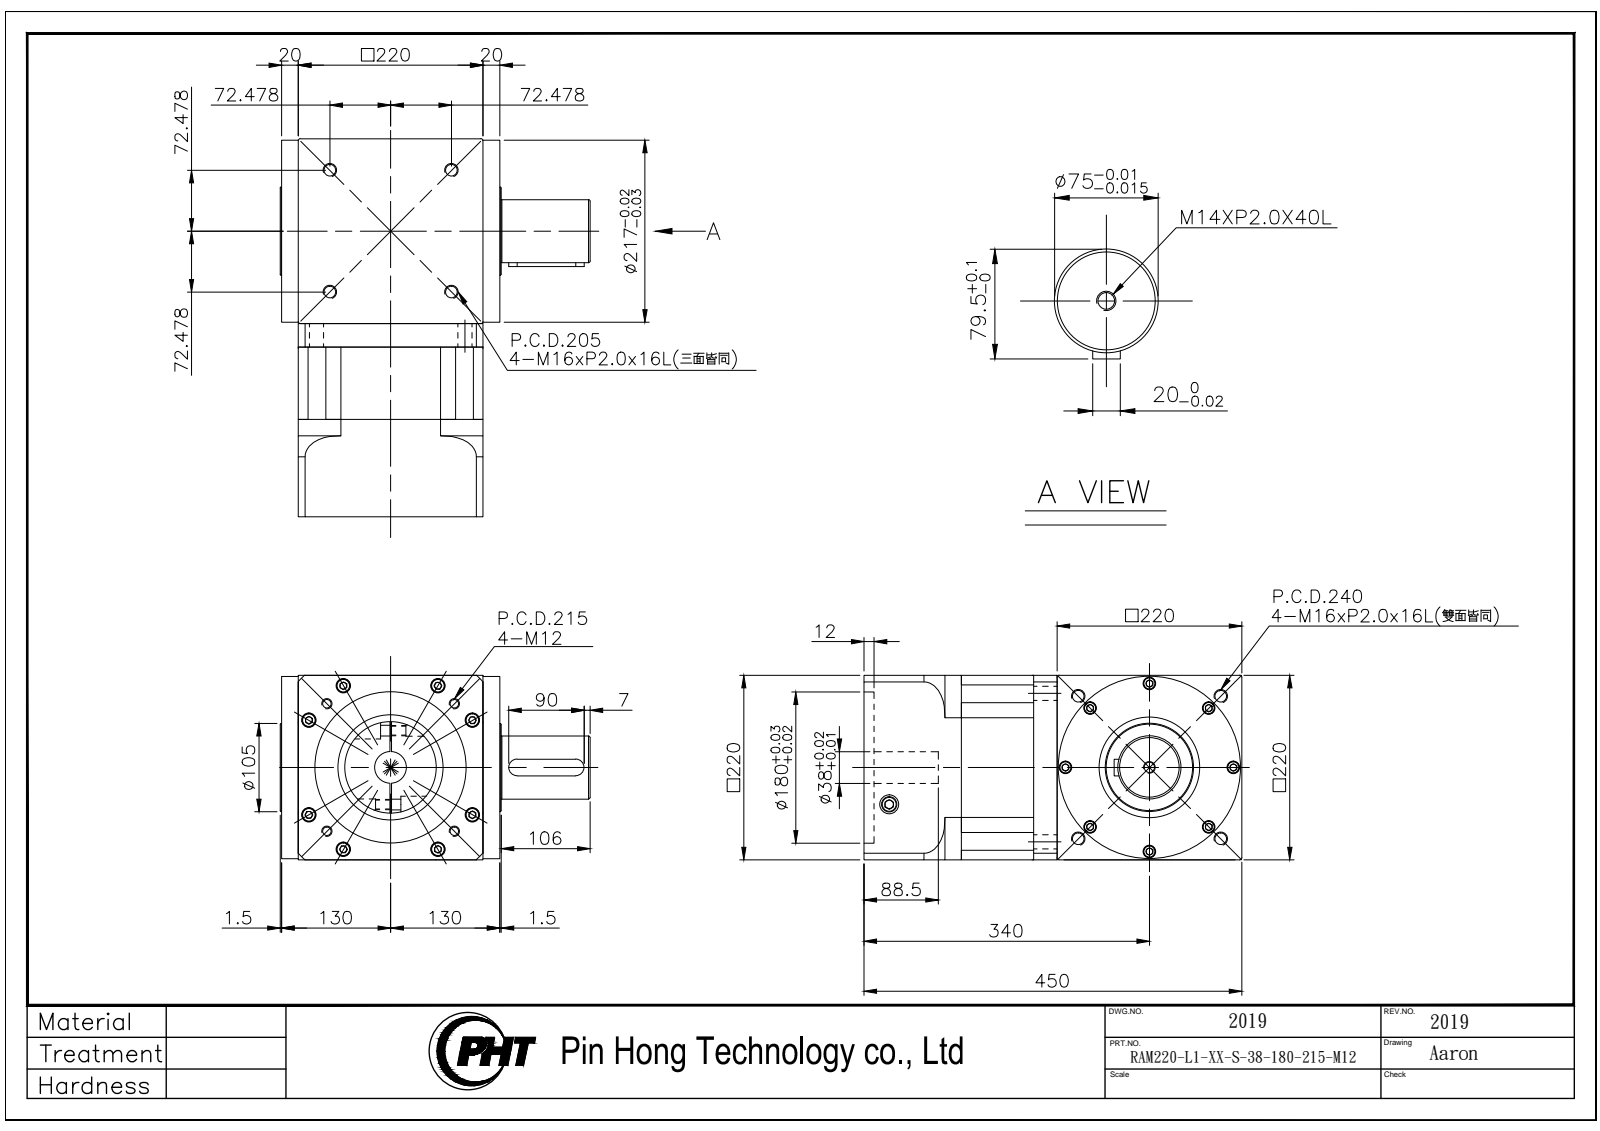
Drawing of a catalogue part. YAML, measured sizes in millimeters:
part_name: "RAM220-L1-XX-S-38-180-215-M12_2019"
step_written_by: "SolidWorks 2016 (AUTOMOTIVE_DESIGN)"
units: millimeters
bodies: {solids: 4, faces: 965, planar: 442, cylindrical: 321, other: 202}
overall_size: [450, 369, 220]
volume: 22610000
surface_area: 1021000
round_holes:
  - {diameter: 9, count: 12}
  - {diameter: 14, count: 12}
  - {diameter: 15, count: 12}
  - {diameter: 17, count: 12}
  - {diameter: 11, count: 8}
  - {diameter: 10.2, count: 4}
  - {diameter: 22.5, count: 2}
  - {diameter: 4, count: 1}
  - {diameter: 12, count: 1}
  - {diameter: 38, count: 1}
  - {diameter: 125, count: 1}
  - {diameter: 180, count: 1}
round_bosses_or_shafts:
  - {diameter: 13, count: 12}
  - {diameter: 16, count: 8}
  - {diameter: 24, count: 4}
  - {diameter: 217, count: 1}
  - {diameter: 120, count: 1}
  - {diameter: 109, count: 1}
  - {diameter: 105, count: 1}
  - {diameter: 75, count: 1}
partial_cylinders:
  - {radius: 15, count: 4}
  - {radius: 10, count: 2}
  - {radius: 125, count: 1}
  - {radius: 150, count: 1}
face_to_face_distances: [220, 86, 114, 28, 334, 248, 20, 240, 129, 43]
hole_center_spacings: [100, 51.76, 112.5, 141.42, 173.2, 193.18, 29.14, 29.76]
